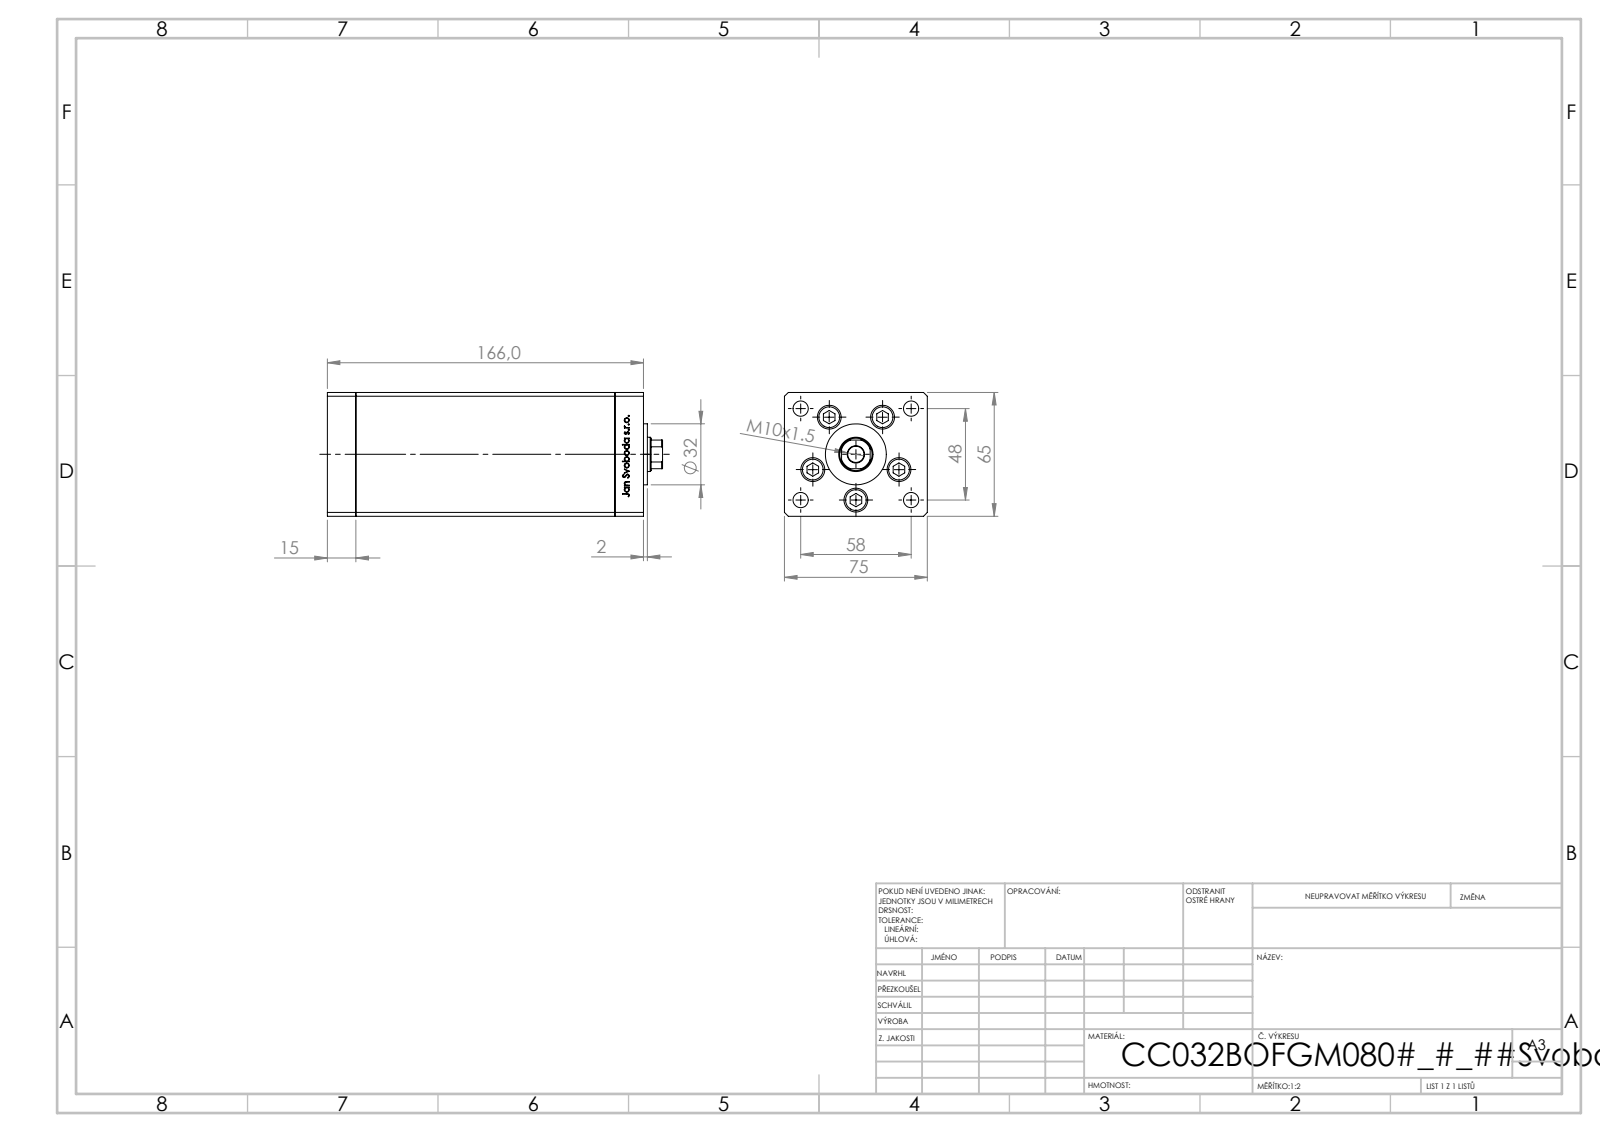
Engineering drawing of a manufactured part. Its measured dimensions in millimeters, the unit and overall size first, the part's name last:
Units: millimetres
Overall size (bounding box): 176 × 75 × 65
Round holes (diameter × count): ⌀9 ×5, ⌀12.5 ×5, ⌀8 ×4, ⌀8.5 ×1, ⌀18 ×1
Round bosses / shafts (diameter × count): ⌀8 ×5, ⌀32 ×1
Partial cylindrical surfaces — rounded edges, fillets, slot ends (radius × count): R0.93 ×2, R8.5 ×1
Main face-to-face distances: 75, 65, 15, 136, 151, 166, 28, 54.5, 10.5, 26.25
Hole centre spacings: 24, 37.64, 15.67, 17.22, 27.71, 28.83, 29, 32.63
Volume: 726 109 mm³ · Surface area: 126 158 mm²
Bodies: 14 solids, 1173 faces (460 planar, 139 cylindrical, 574 other)
Part name (STEP PRODUCT): V220C_B MIDDLE; V220C_VC_B; V220C_FRONT_B; V220C BACK_B (+1 more)
STEP written by: SolidWorks 2019 (CONFIG_CONTROL_DESIGN)
